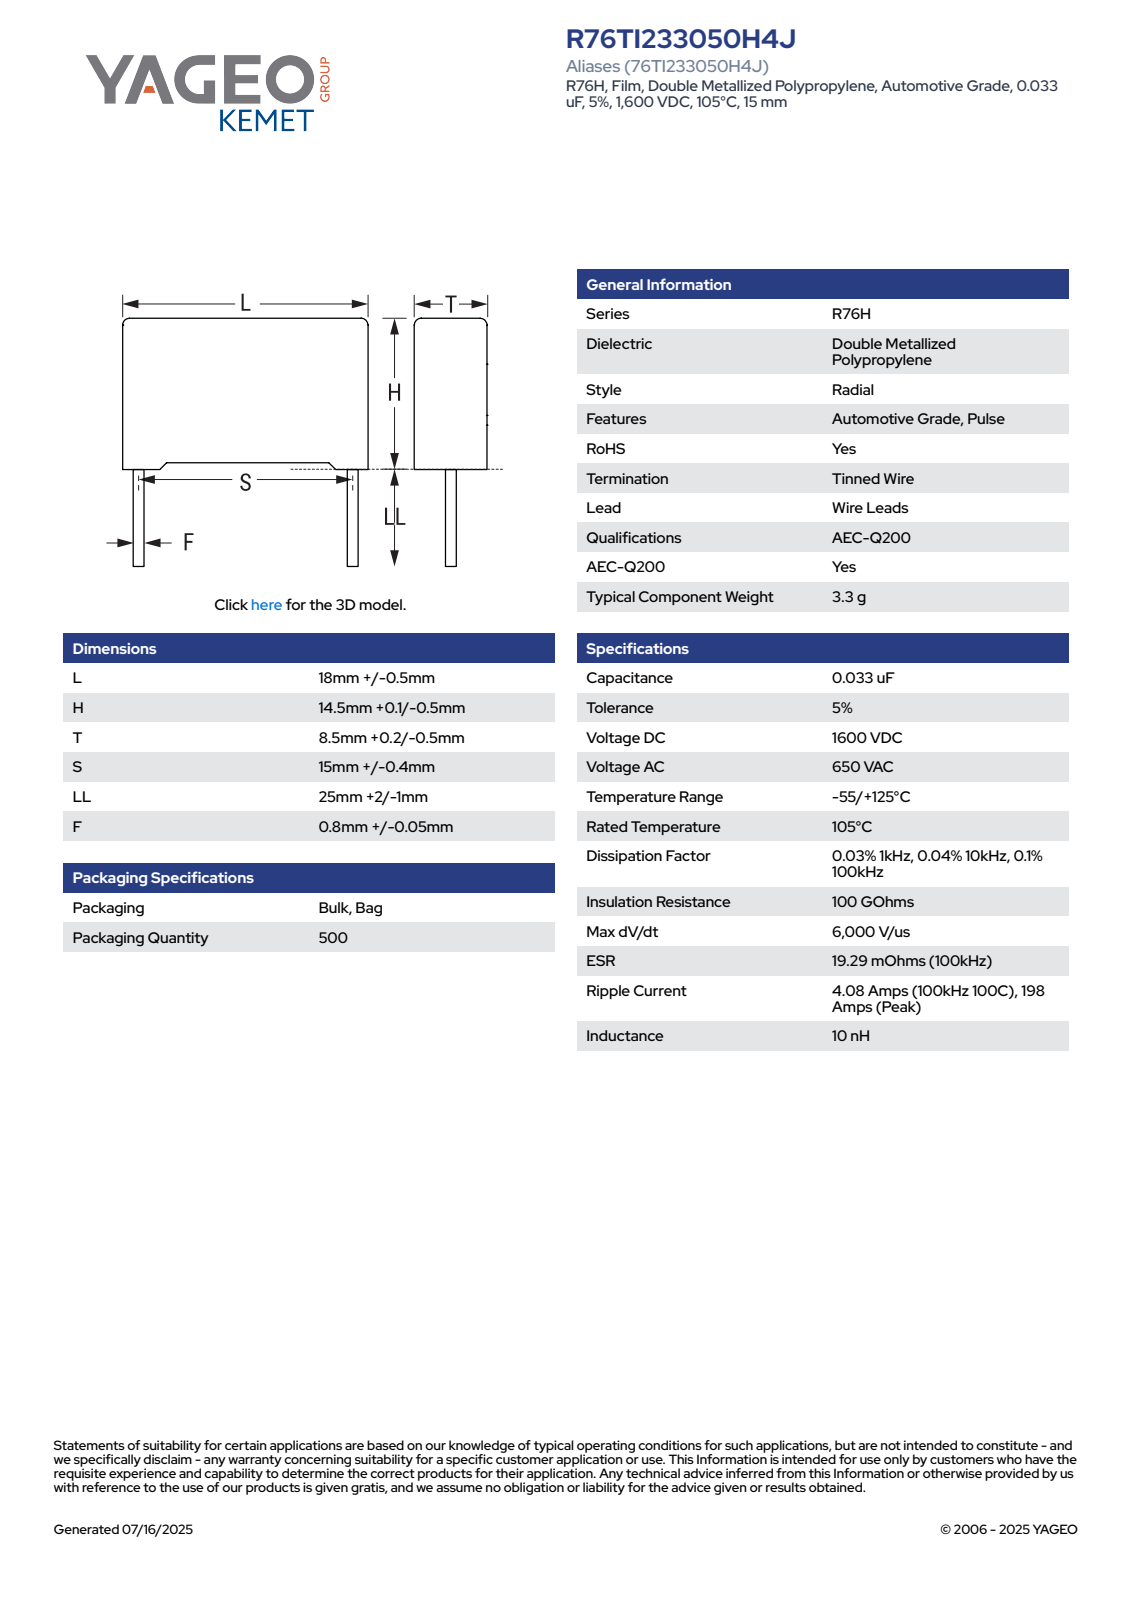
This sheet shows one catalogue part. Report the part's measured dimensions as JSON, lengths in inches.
{"part_name": "CFR_RB2R76_18X14.5X8.5_L18.5H14.6T8.7S15LL27F0.85", "step_written_by": "SolidWorks 2014 (AUTOMOTIVE_DESIGN)", "units": "inches", "bodies": {"solids": 4, "faces": 85, "planar": 77, "cylindrical": 8, "other": 0}, "overall_size": [1.638, 0.728, 0.343], "volume_in3": 0.139, "surface_area_in2": 2.004, "round_bosses_or_shafts": [[0.033, 2]], "partial_cylinders_radius": [[0.02, 4]], "face_to_face_distances": [0.343, 0.545, 0.728, 0.024, 0.03, 0.575, 0.318, 0.02, 0.555, 0.704]}
